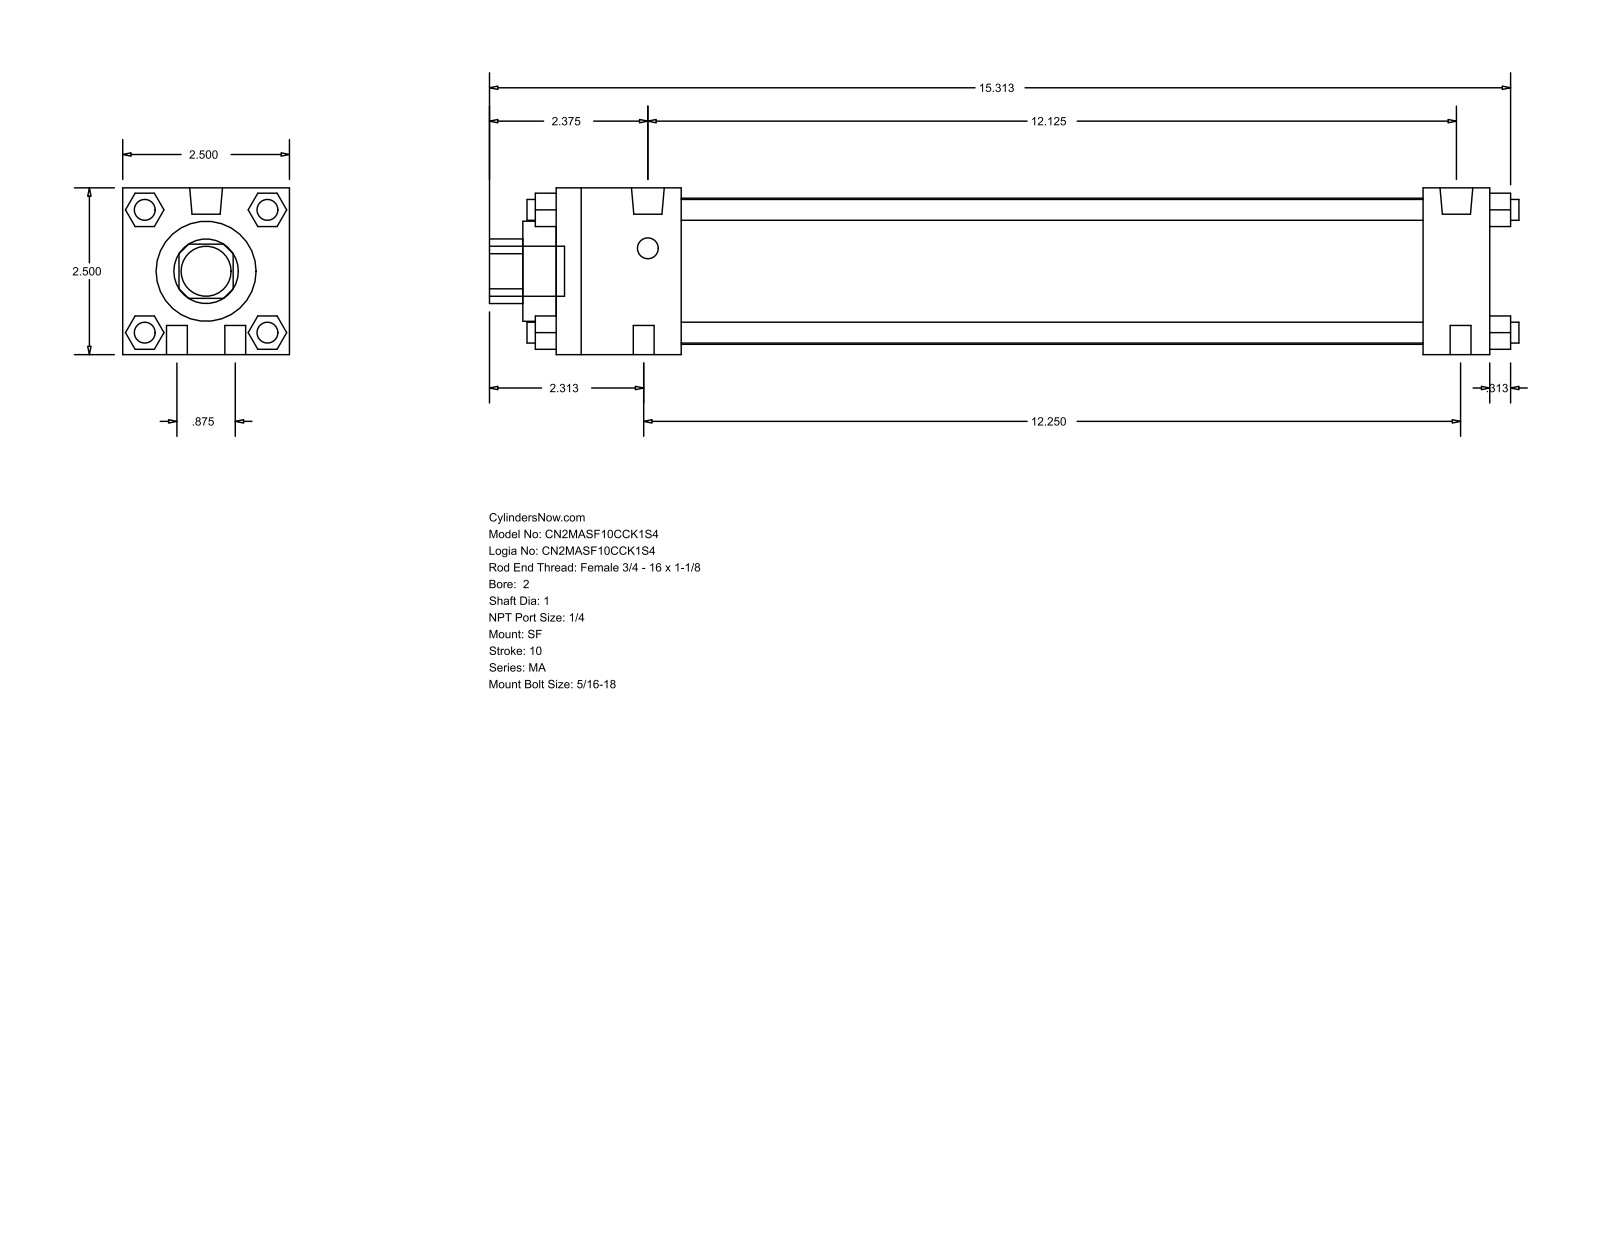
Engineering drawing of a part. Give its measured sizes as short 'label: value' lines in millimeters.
name: MA_SF__0200_1
written by: GSSL Pune (CONFIG_CONTROL_DESIGN)
unit: mm
bodies: 0 solids, 124 faces (94 planar, 30 cylindrical, 0 other)
size: 392.11 × 63.5 × 63.5
holes: 1× ⌀25.4, 1× ⌀38.1, 1× ⌀55.63
bosses: 10× ⌀7.94, 2× ⌀12.49, 1× ⌀19.05
rounds: 1× R12.29
face distances: 63.5, 355.6, 12.7, 25.4, 330.2, 47.63, 282.57, 307.97, 40.47, 23.37
